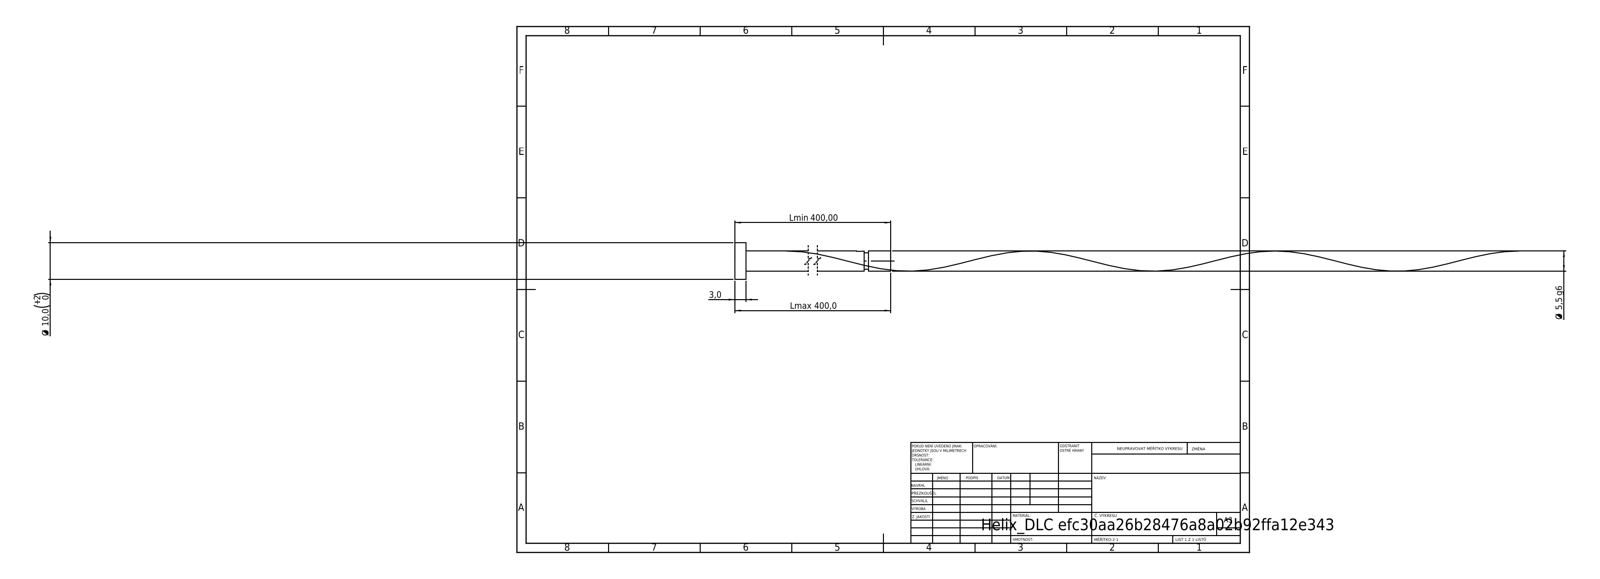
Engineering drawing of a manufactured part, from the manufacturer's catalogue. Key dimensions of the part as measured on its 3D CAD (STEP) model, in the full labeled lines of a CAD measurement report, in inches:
STEP written by: SolidWorks 2019 (CONFIG_CONTROL_DESIGN)
Units: inches
Bodies: 1 solid, 16 faces (6 planar, 9 cylindrical, 1 other)
Overall size (bounding box): 15.748 × 0.394 × 0.394
Volume: 0.713 in³ · Surface area: 14.78 in²
Round bosses / shafts (diameter × count): ⌀0.394 ×1, ⌀0.217 ×1, ⌀0.173 ×1
Main face-to-face distances: 0.118, 15.748, 15.63, 15.507, 15.389, 0.241, 15.464, 15.346, 0.043, 0.284
